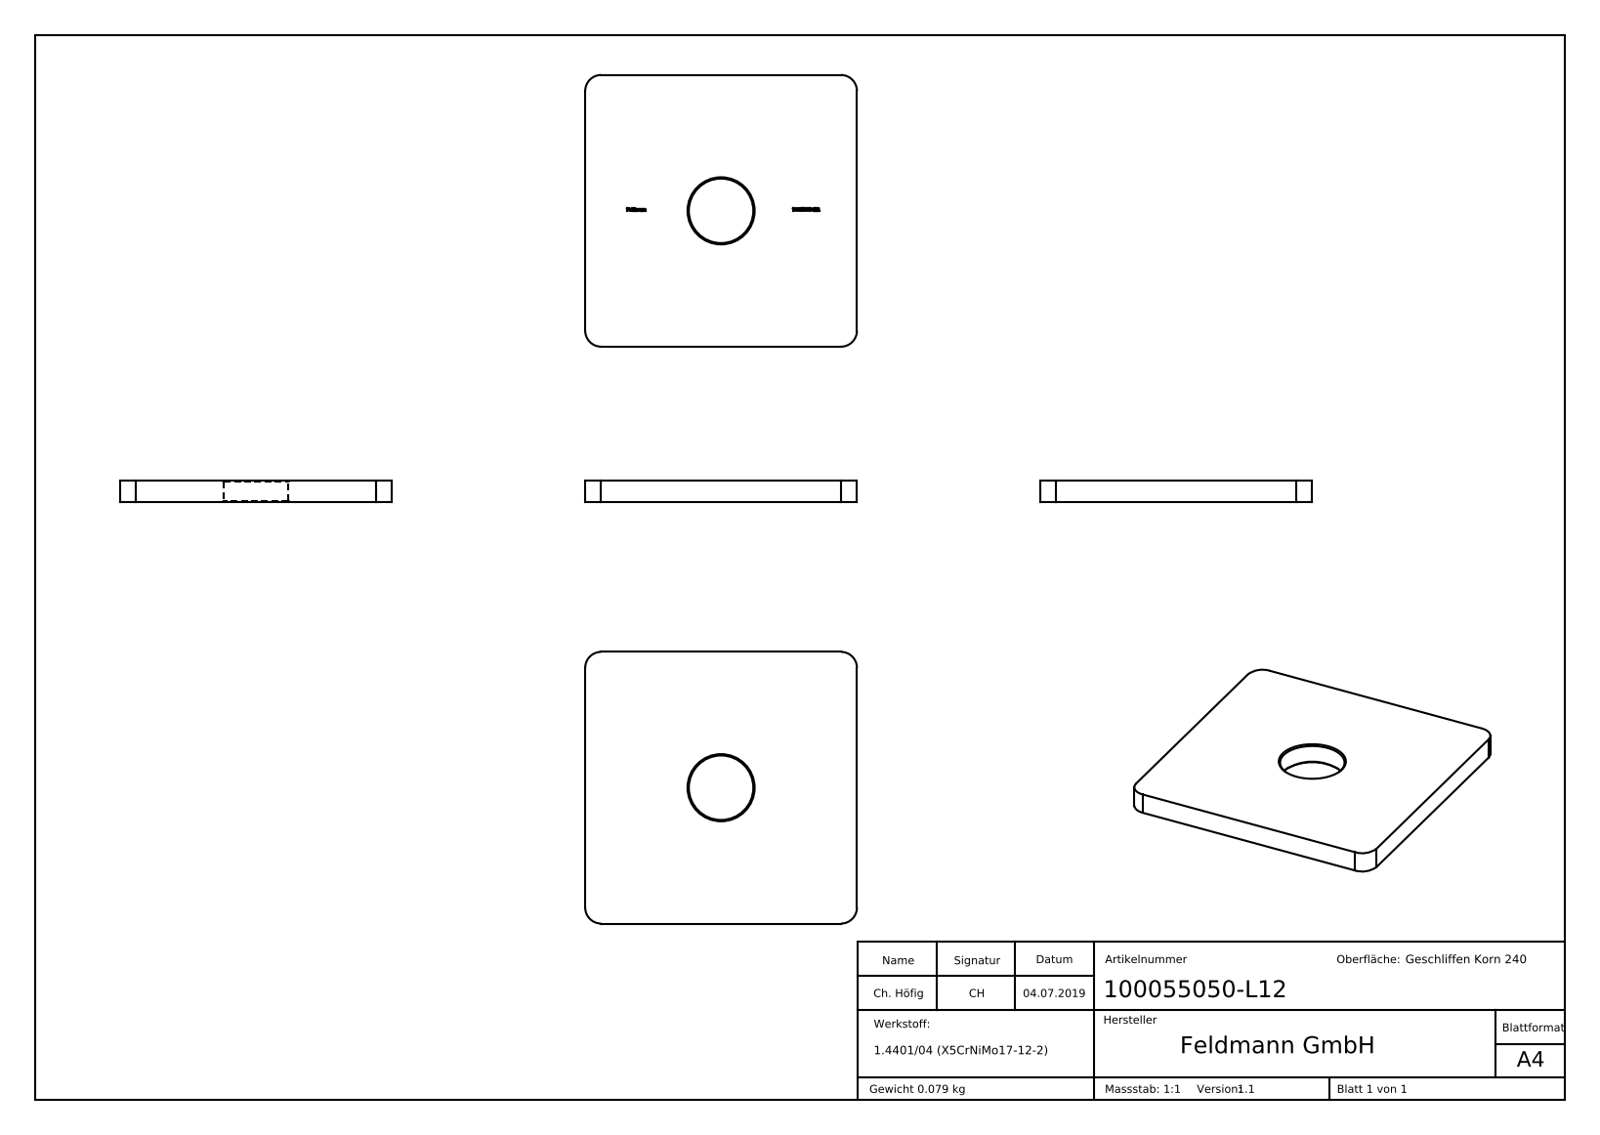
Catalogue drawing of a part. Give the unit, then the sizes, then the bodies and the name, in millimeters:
Units: millimetres
Overall size (bounding box): 51 × 51 × 4
Round holes (diameter × count): ⌀12.1 ×1
Partial cylindrical surfaces — rounded edges, fillets, slot ends (radius × count): R3 ×4
Main face-to-face distances: 4, 51, 3.9, 25.5, 0.53, 26.03, 24.97, 0.5, 34.11, 30.36
Volume: 9 911 mm³ · Surface area: 5 898 mm²
Bodies: 1 solid, 268 faces (135 planar, 6 cylindrical, 127 other)
Part name (STEP PRODUCT): 100055050-L12
STEP written by: SolidWorks 2015 (CONFIG_CONTROL_DESIGN)
